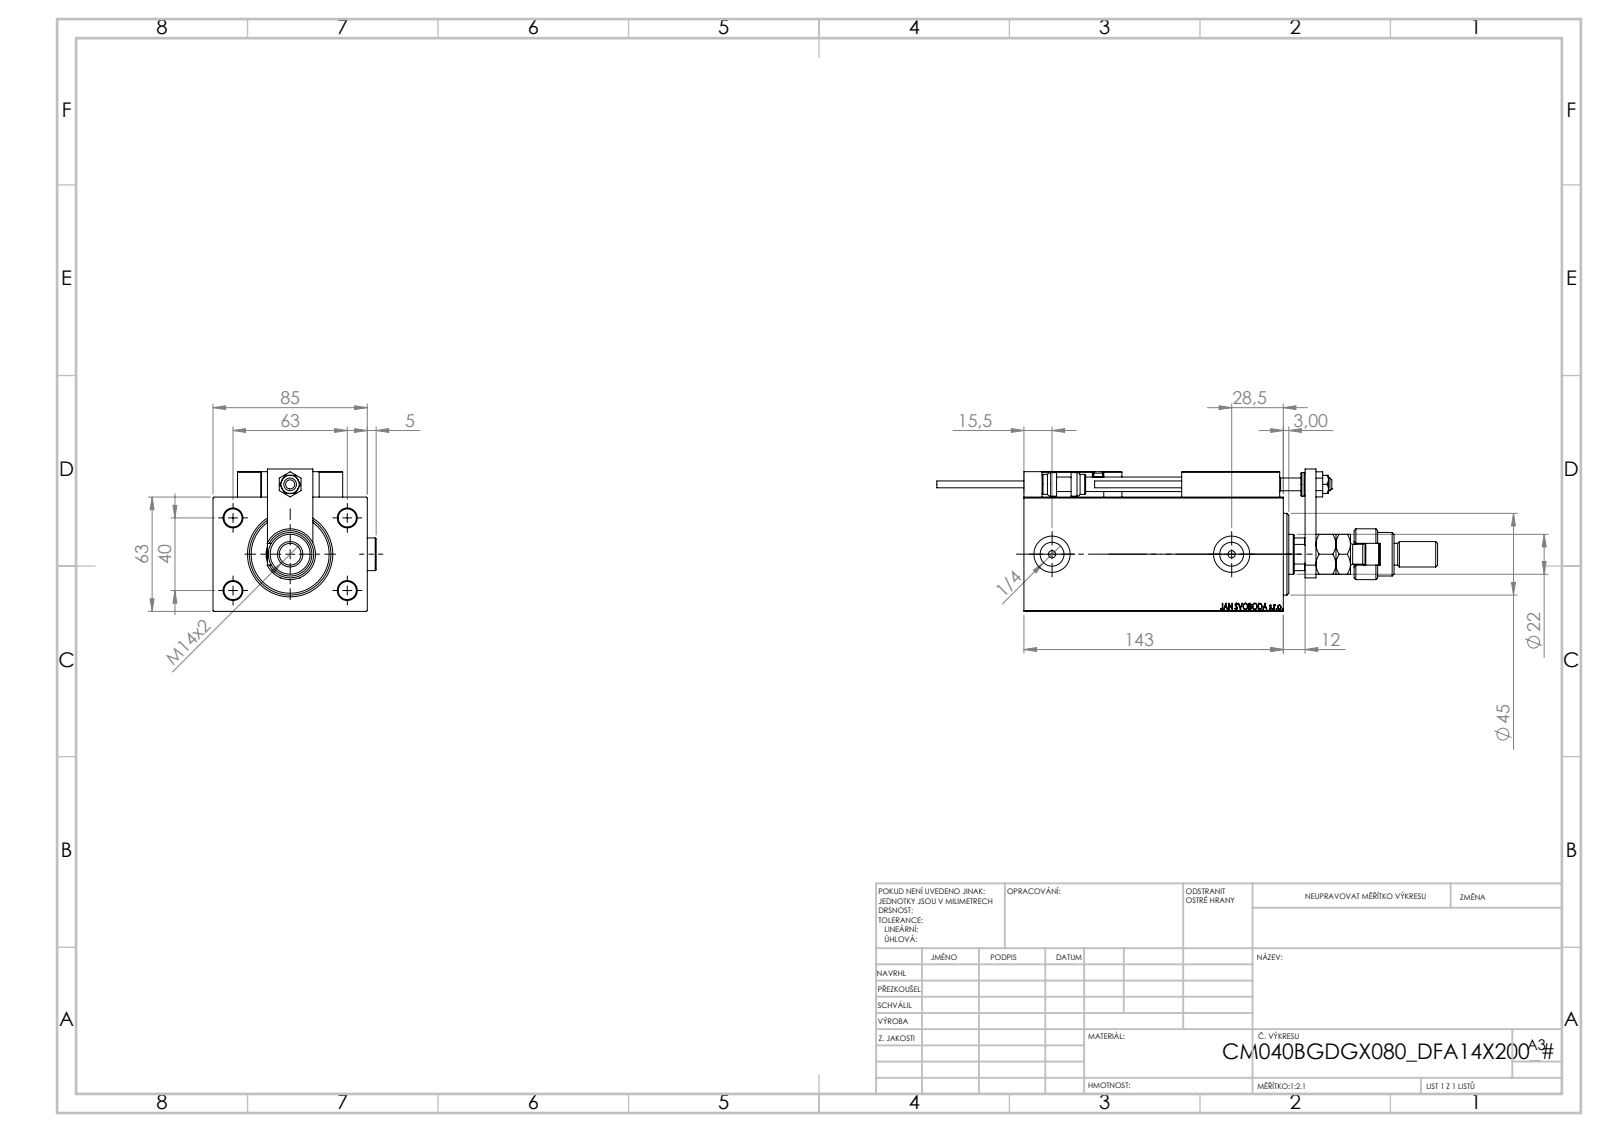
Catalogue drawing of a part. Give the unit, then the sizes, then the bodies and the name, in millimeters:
Units: millimetres
Overall size (bounding box): 276 × 89.9 × 78.5
Round holes (diameter × count): ⌀4 ×6, ⌀8 ×5, ⌀3.2 ×4, ⌀10 ×4, ⌀5 ×2, ⌀13.16 ×2, ⌀20 ×2, ⌀7 ×1, ⌀12.5 ×1, ⌀16.5 ×1, ⌀22 ×1, ⌀25.5 ×1
Round bosses / shafts (diameter × count): ⌀18 ×3, ⌀11 ×2, ⌀5 ×2, ⌀3.8 ×2, ⌀28 ×1, ⌀24 ×1, ⌀14 ×1, ⌀13 ×1
Partial cylindrical surfaces — rounded edges, fillets, slot ends (radius × count): R0.3 ×30, R3 ×2, R9.75 ×1, R10.5 ×1
Main face-to-face distances: 63, 85, 12, 131, 143, 14, 77, 30, 18, 15
Hole centre spacings: 37.31, 11.37, 20, 29.59, 29.69, 36.06, 36.53, 40
Volume: 755 384 mm³ · Surface area: 133 823 mm²
Bodies: 28 solids, 1457 faces (623 planar, 213 cylindrical, 621 other)
Part name (STEP PRODUCT): SWITCH_X_FRONT_BACK; MAGNET; SWITCH X; TYC_L79 (+8 more)
STEP written by: SolidWorks 2019 (CONFIG_CONTROL_DESIGN)
